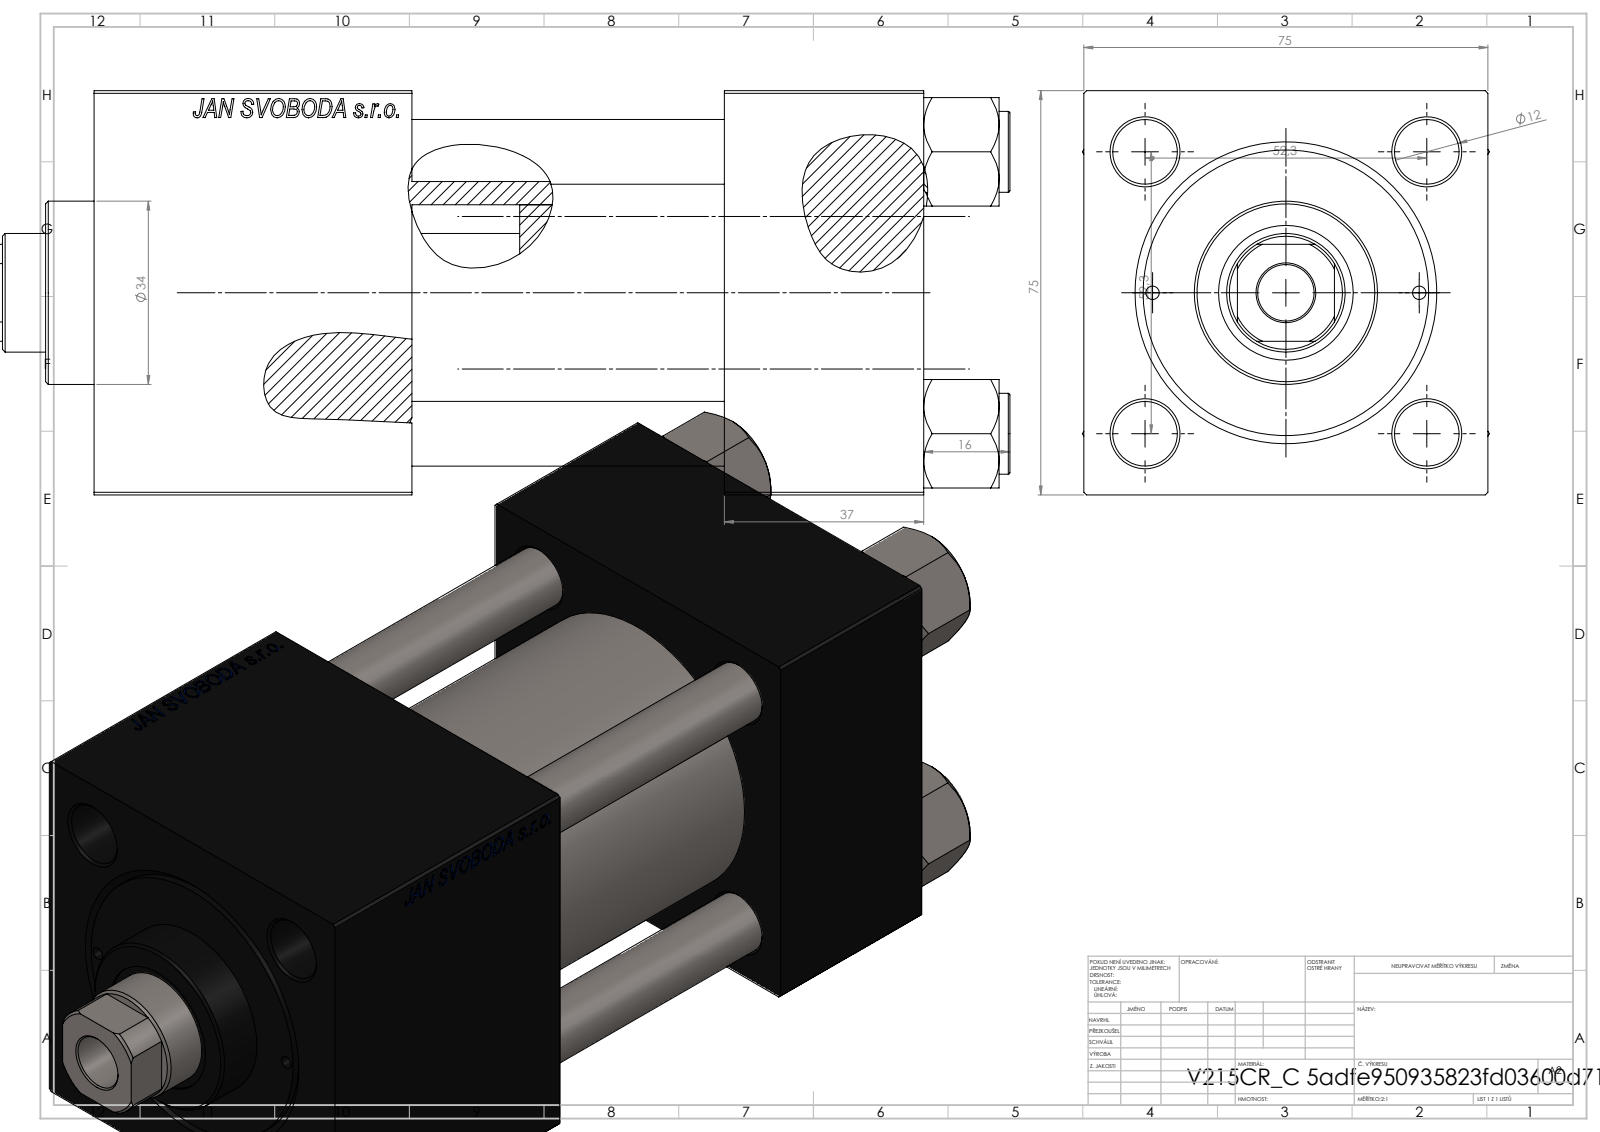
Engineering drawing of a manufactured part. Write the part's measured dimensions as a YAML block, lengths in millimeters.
part_name: "V215_VC_A; V215CR_C_TYCINKA; V215CR_C_Body; V215CR_VCP_C (+1 more)"
step_written_by: "SolidWorks 2019 (CONFIG_CONTROL_DESIGN)"
units: millimeters
bodies: {solids: 11, faces: 1154, planar: 528, cylindrical: 90, other: 536}
overall_size: [195, 75.54, 75]
volume: 656915
surface_area: 147364
round_holes:
  - {diameter: 12, count: 4}
  - {diameter: 2.5, count: 2}
  - {diameter: 7, count: 2}
  - {diameter: 20.96, count: 2}
  - {diameter: 30, count: 2}
  - {diameter: 10.5, count: 1}
  - {diameter: 22, count: 1}
  - {diameter: 25, count: 1}
  - {diameter: 41, count: 1}
  - {diameter: 50, count: 1}
  - {diameter: 53, count: 1}
round_bosses_or_shafts:
  - {diameter: 15, count: 4}
  - {diameter: 56, count: 1}
  - {diameter: 34, count: 1}
partial_cylinders:
  - {radius: 10.5, count: 1}
face_to_face_distances: [75, 37, 154, 117, 95, 58, 59, 125.3, 88.3, 30.3]
hole_center_spacings: [26.19, 36.98, 52.3, 57.22, 24.75, 73.96, 49.5, 93.5]
